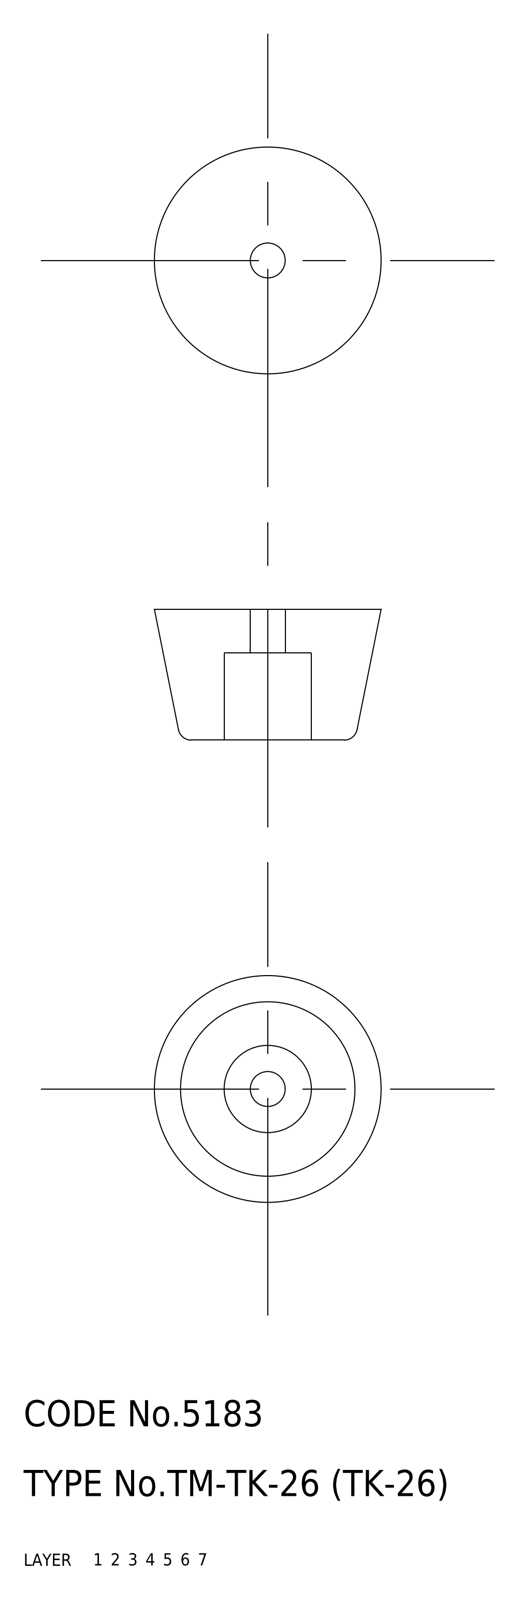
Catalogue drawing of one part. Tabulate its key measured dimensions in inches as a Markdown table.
| quantity | value |
| --- | --- |
| part name | washer; rubber foot; TK_26_9519_36 |
| STEP written by | CADfix (AUTOMOTIVE_DESIGN) |
| units | inches |
| bodies | 2 solids, 20 faces (0 planar, 0 cylindrical, 20 other) |
| overall size | 1.024 × 1.024 × 0.591 |
| volume | 0.33 in³ |
| surface area | 4.042 in² |
